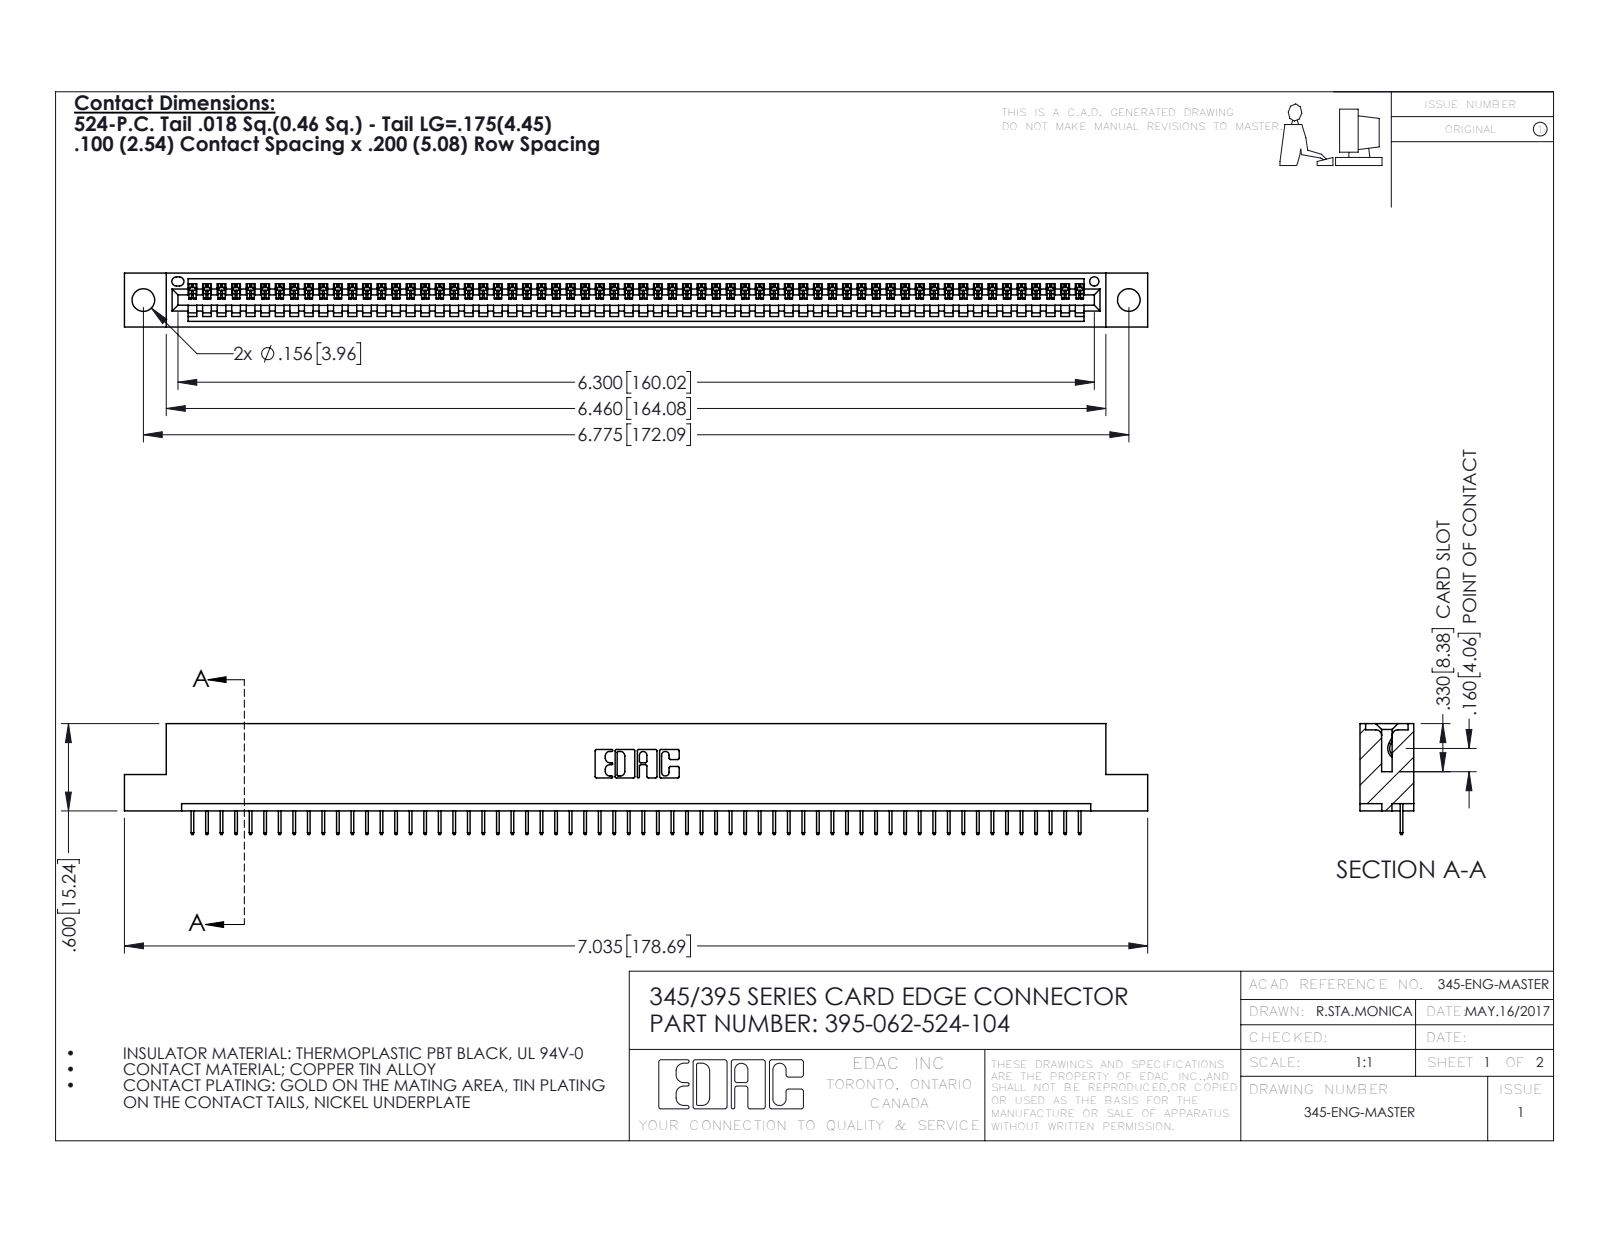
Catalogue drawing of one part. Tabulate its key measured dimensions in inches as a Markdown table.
| quantity | value |
| --- | --- |
| part name | 395-062-524-104; 345 Part_Flush Mounting Lugs - 0.156 Dia-TH; 345-292-001_345-293-124 |
| STEP written by | SolidWorks 2016 (CONFIG_CONTROL_DESIGN) |
| units | inches |
| bodies | 63 solids, 3970 faces (2932 planar, 1038 cylindrical, 0 other) |
| overall size | 7.035 × 0.762 × 0.37 |
| volume | 1.025 in³ |
| surface area | 33.52 in² |
| round holes (diameter × count) | 0.156 × 2, 0.064 × 1 |
| partial cylindrical surfaces (radius × count) | 0.006 × 124, 0.01 × 22, 0.007 × 6, 0.031 × 6, 0.026 × 3, 0.031 × 2, 0.04 × 2, 0.014 × 1 |
| main face-to-face distances | 0.072, 0.298, 0.37, 0.2, 0.098, 0.272, 0.025, 0.225, 0.072, 0.149 |
| hole center spacings | 0.27, 6.539, 6.775 |
